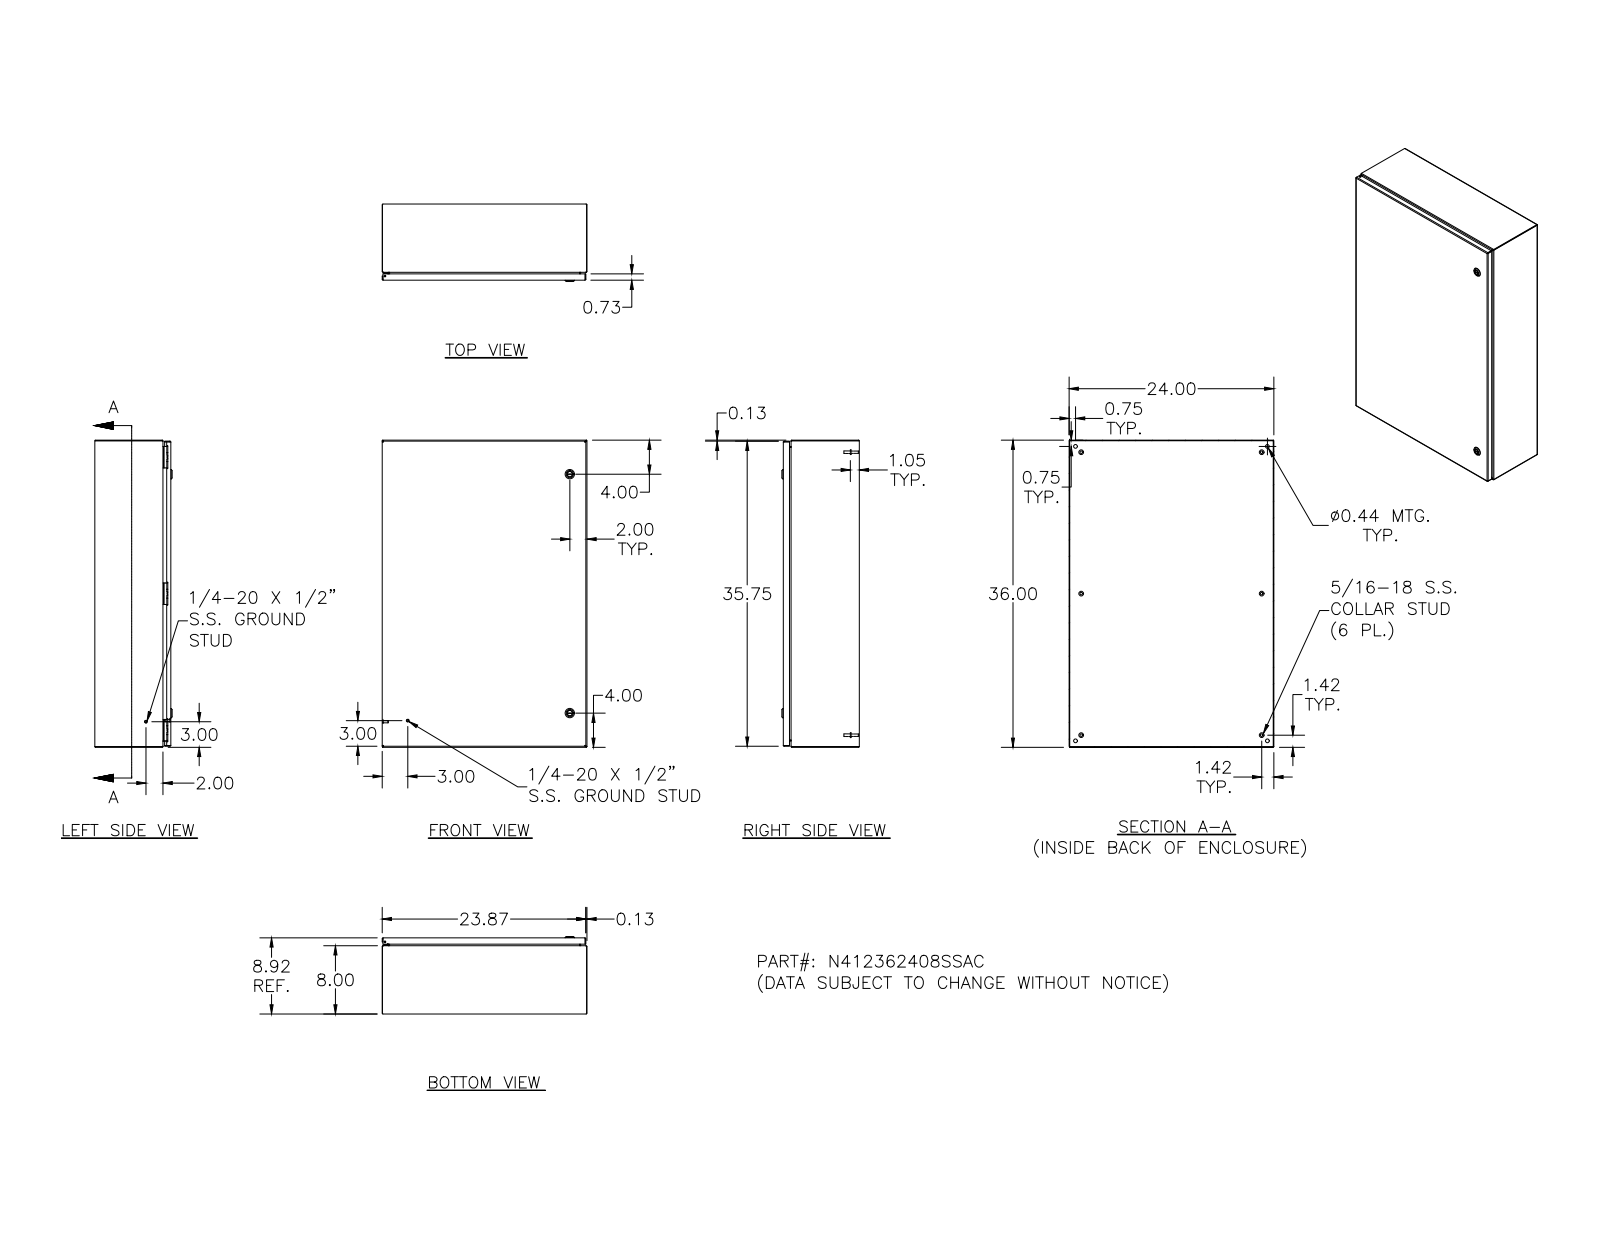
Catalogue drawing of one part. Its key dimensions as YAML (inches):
part_name: "N412362408SSAC; N412362408SSACBKP; 388151; N4123624SSACLID (+8 more)"
step_written_by: "Autodesk Inventor 2011 (AUTOMOTIVE_DESIGN)"
units: inches
bodies: {solids: 53, faces: 2098, planar: 823, cylindrical: 766, other: 509}
overall_size: [36, 24, 9.075]
volume: 217.9
surface_area: 5913
round_holes:
  - {diameter: 0.188, count: 7}
  - {diameter: 0.093, count: 6}
  - {diameter: 0.152, count: 6}
  - {diameter: 0.167, count: 6}
  - {diameter: 0.172, count: 6}
  - {diameter: 0.437, count: 4}
  - {diameter: 0.156, count: 3}
  - {diameter: 0.197, count: 2}
  - {diameter: 0.315, count: 2}
  - {diameter: 0.394, count: 2}
  - {diameter: 0.402, count: 2}
  - {diameter: 0.634, count: 2}
round_bosses_or_shafts:
  - {diameter: 0.25, count: 14}
  - {diameter: 0.563, count: 6}
  - {diameter: 0.36, count: 6}
  - {diameter: 0.32, count: 6}
  - {diameter: 0.3, count: 6}
  - {diameter: 0.275, count: 6}
  - {diameter: 0.256, count: 6}
  - {diameter: 0.164, count: 6}
partial_cylinders:
  - {radius: 0.05, count: 38}
  - {radius: 0.016, count: 26}
  - {radius: 0.125, count: 21}
  - {radius: 0.031, count: 18}
  - {radius: 0.016, count: 16}
  - {radius: 0.09, count: 16}
  - {radius: 0.02, count: 15}
  - {radius: 0.032, count: 12}
face_to_face_distances: [0.074, 8.843, 8.769, 8.917, 23.926, 35.926, 23.852, 24, 36, 35.852]
hole_center_spacings: [16.004, 32, 15.996, 0.017, 0.66, 15.992, 16, 16.008]
